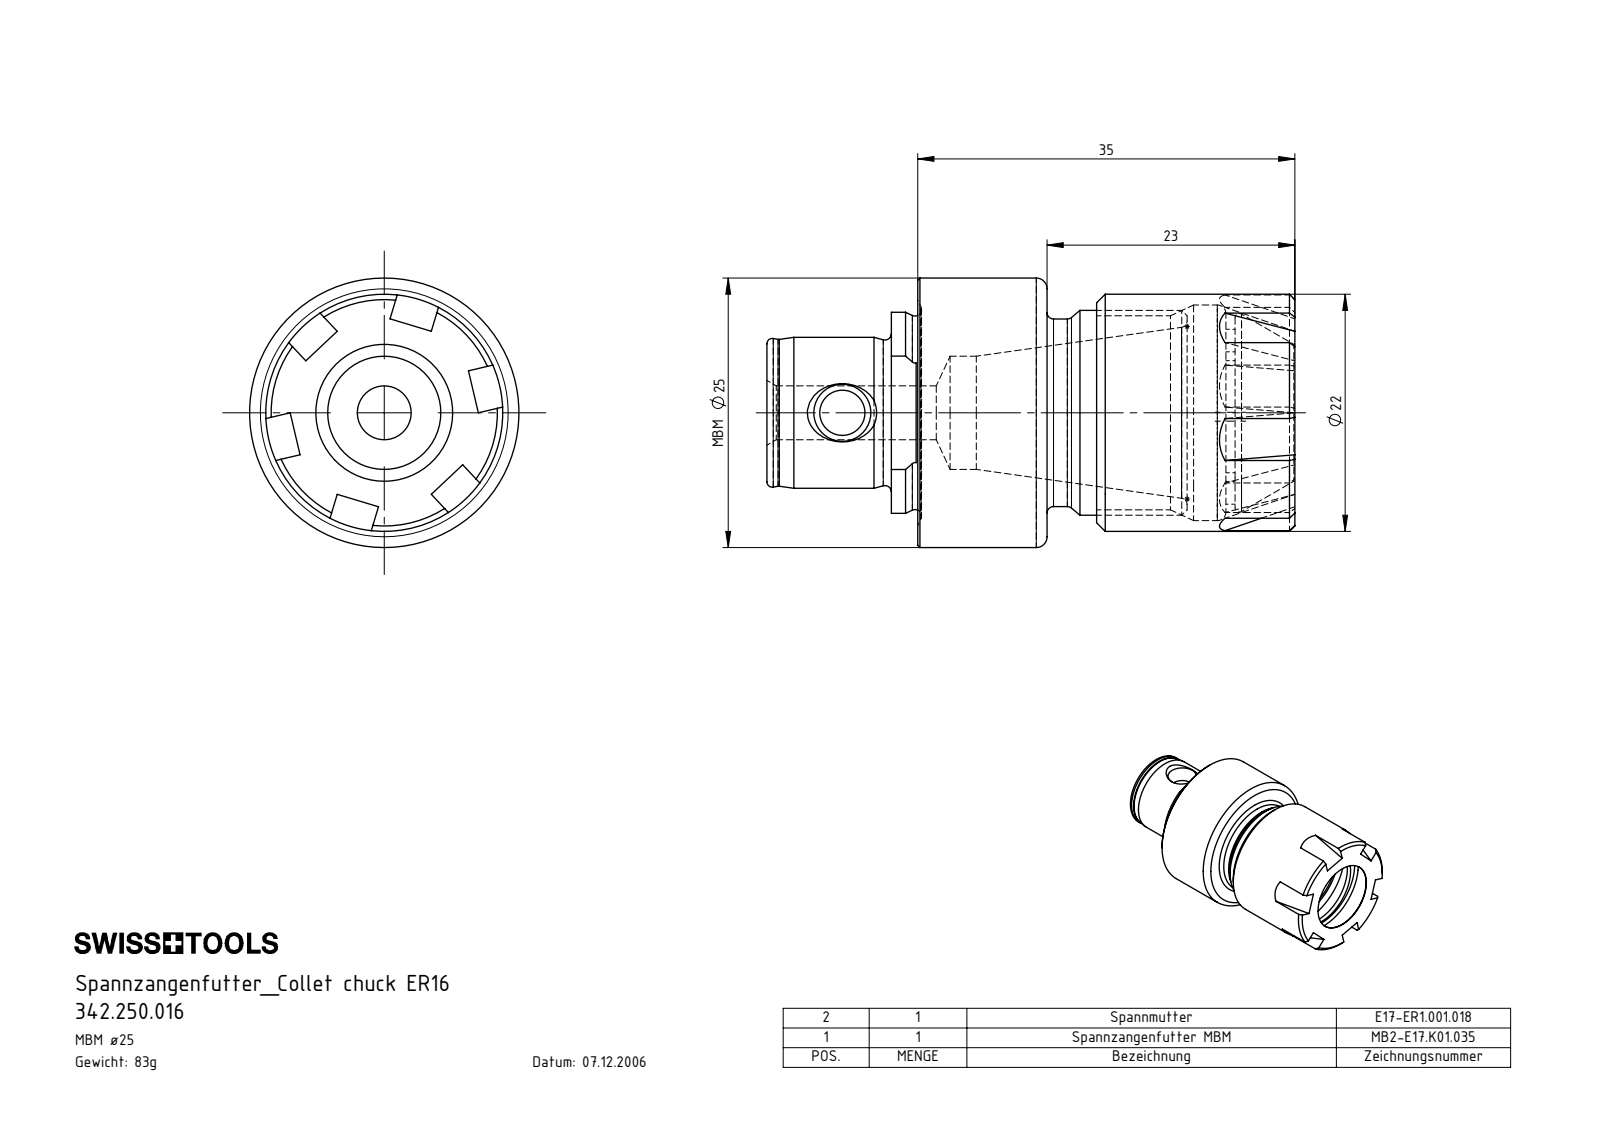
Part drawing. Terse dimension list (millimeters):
name: MB2-E17.K01.035_C; 342.250.016; E17-ER1.001.018
written by: SolidWorks 2017 (CONFIG_CONTROL_DESIGN)
unit: mm
bodies: 2 solids, 129 faces (33 planar, 28 cylindrical, 68 other)
size: 49 × 25 × 25
volume: 10 585 mm³; area: 7 205 mm²
holes: 1× ⌀4.2, 1× ⌀5, 1× ⌀10.5, 1× ⌀12.7, 1× ⌀18, 1× ⌀20
bosses: 1× ⌀25, 1× ⌀22, 1× ⌀19, 1× ⌀17.4, 1× ⌀14
rounds: 2× R7.7, 1× R9.32
face distances: 12, 23, 16.6, 35, 14, 26, 49, 11.55, 2.45, 14.45
